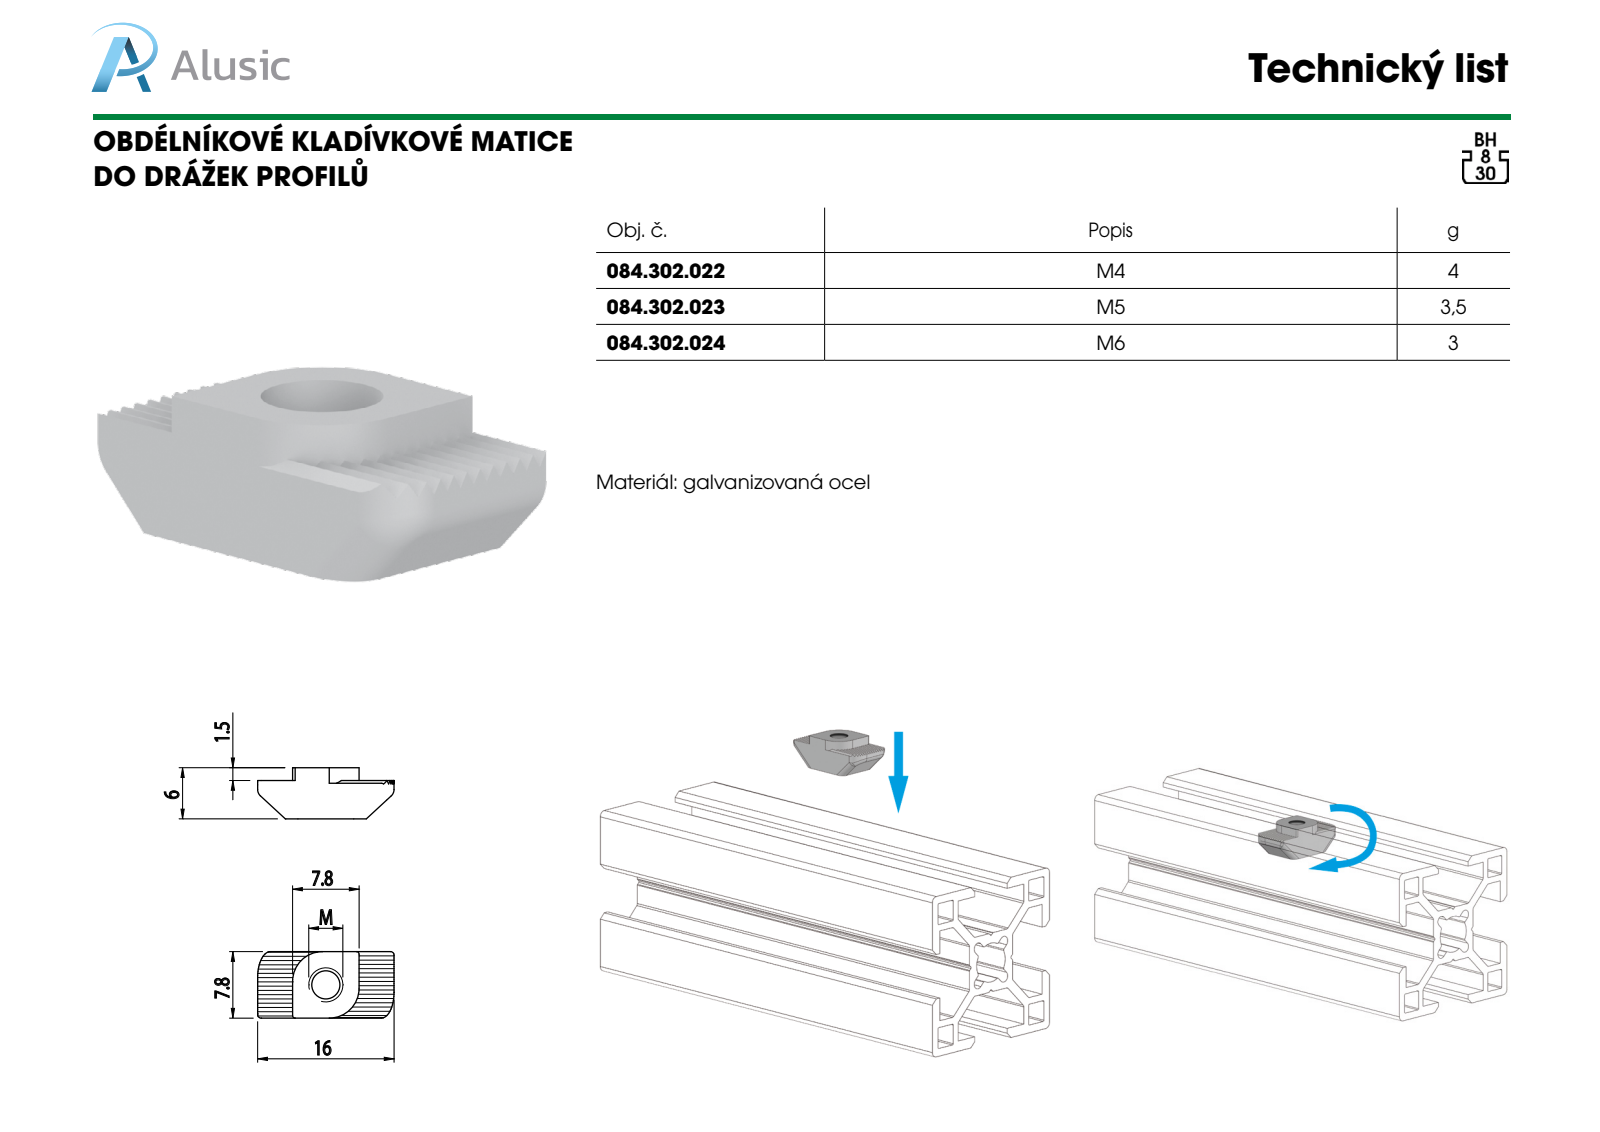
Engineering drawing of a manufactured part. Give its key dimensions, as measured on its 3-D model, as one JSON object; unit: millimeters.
{"part_name": "084.302.022", "step_written_by": "SolidWorks 2012 (CONFIG_CONTROL_DESIGN)", "units": "millimeters", "bodies": {"solids": 1, "faces": 86, "planar": 74, "cylindrical": 10, "other": 2}, "overall_size": [15.5, 7.7, 6], "volume_mm3": 478, "surface_area_mm2": 530, "round_holes": [[3.3, 1]], "partial_cylinders_radius": [[1, 4], [2.5, 2], [3.5, 2]], "face_to_face_distances": [7.7, 6, 0.85, 0.42, 1.27, 2.12, 4.07, 0.43, 1.69, 4.24]}
